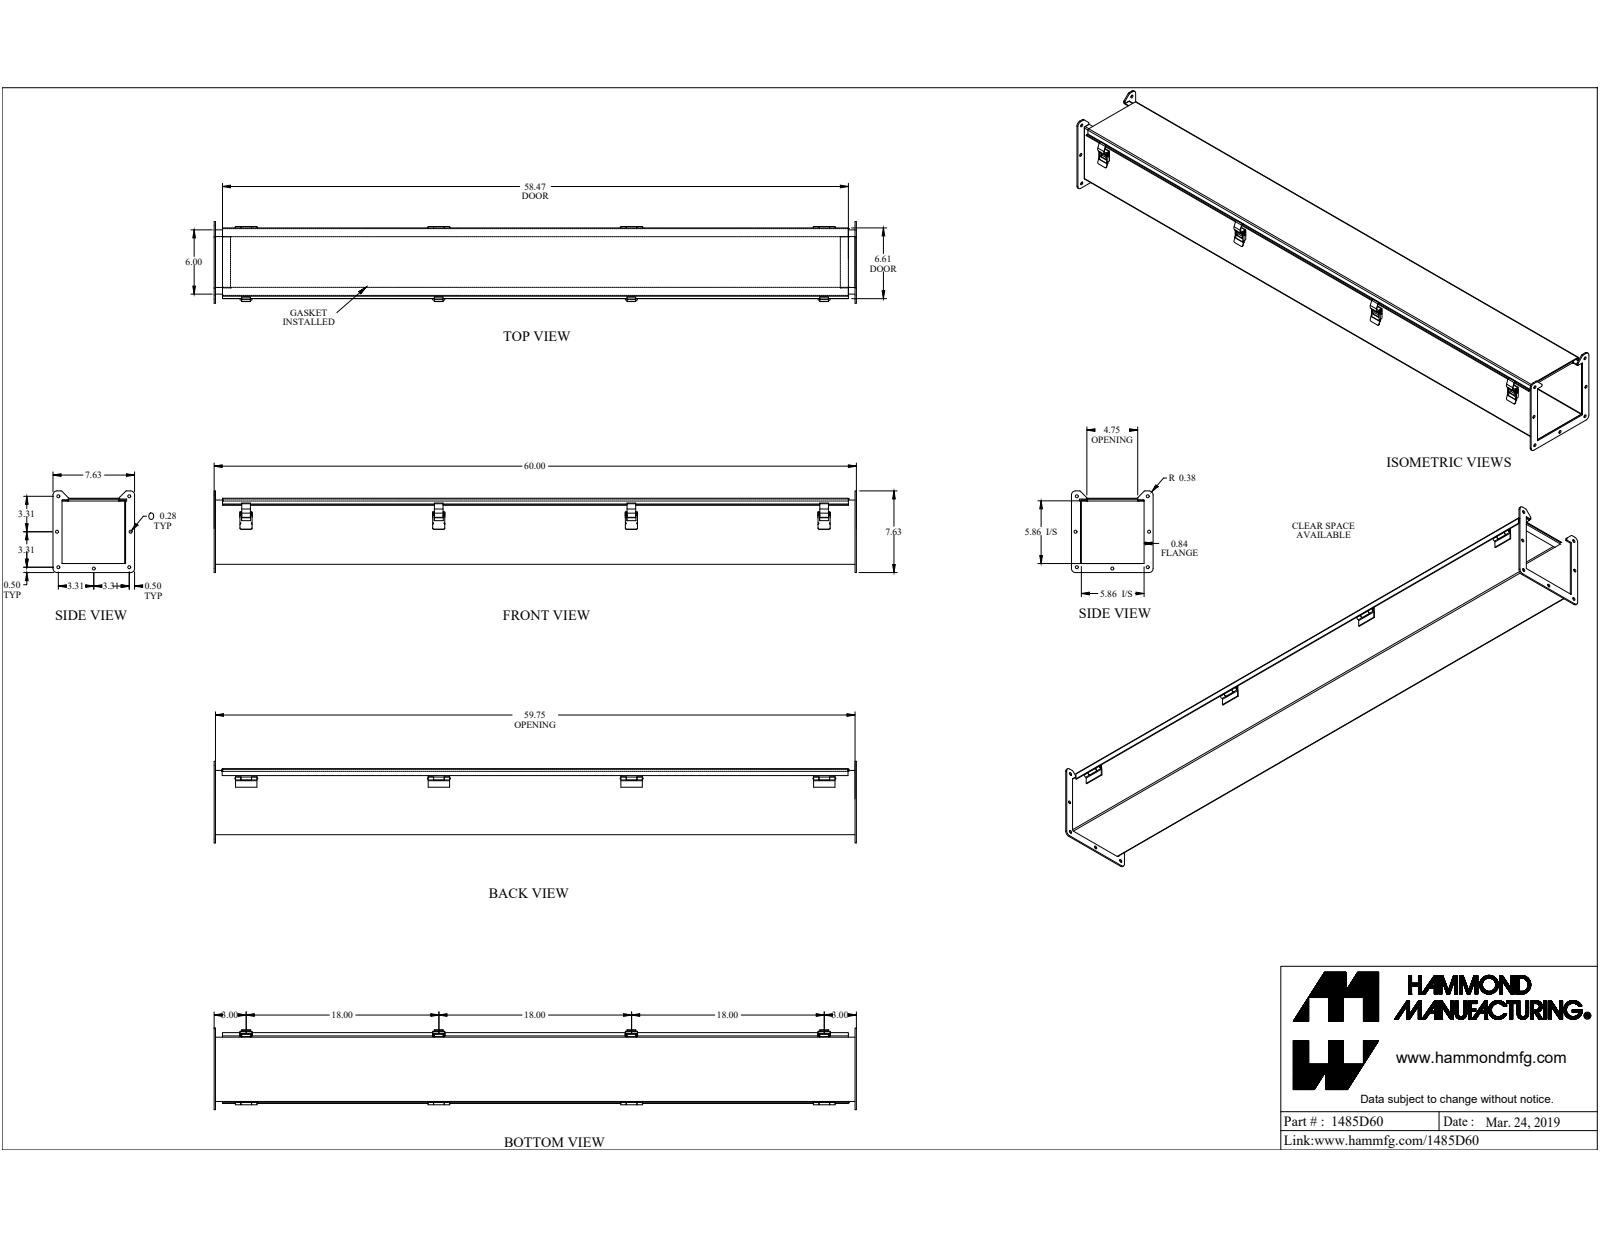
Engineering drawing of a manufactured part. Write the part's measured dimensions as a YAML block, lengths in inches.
part_name: "1485D60"
step_written_by: "SolidWorks 2019 (CONFIG_CONTROL_DESIGN)"
units: inches
bodies: {solids: 32, faces: 706, planar: 418, cylindrical: 280, other: 8}
overall_size: [60, 7.625, 7.625]
volume: 137.9
surface_area: 3573
round_holes:
  - {diameter: 0.281, count: 7}
  - {diameter: 0.125, count: 1}
  - {diameter: 0.13, count: 1}
  - {diameter: 0.164, count: 1}
round_bosses_or_shafts:
  - {diameter: 0.187, count: 2}
  - {diameter: 0.275, count: 1}
  - {diameter: 0.156, count: 1}
  - {diameter: 0.125, count: 1}
  - {diameter: 0.125, count: 1}
partial_cylinders:
  - {radius: 0.016, count: 25}
  - {radius: 0.125, count: 13}
  - {radius: 0.035, count: 9}
  - {radius: 0.039, count: 9}
  - {radius: 0.076, count: 9}
  - {radius: 0.015, count: 8}
  - {radius: 0.029, count: 8}
  - {radius: 0.086, count: 8}
face_to_face_distances: [0.072, 5.928, 6.1, 6, 5.856, 6.028, 6.172, 0.172, 5.913, 5.841]
hole_center_spacings: [7.519, 6.625, 3.315, 3.315, 9.369, 0.285, 1.112, 1.459]
